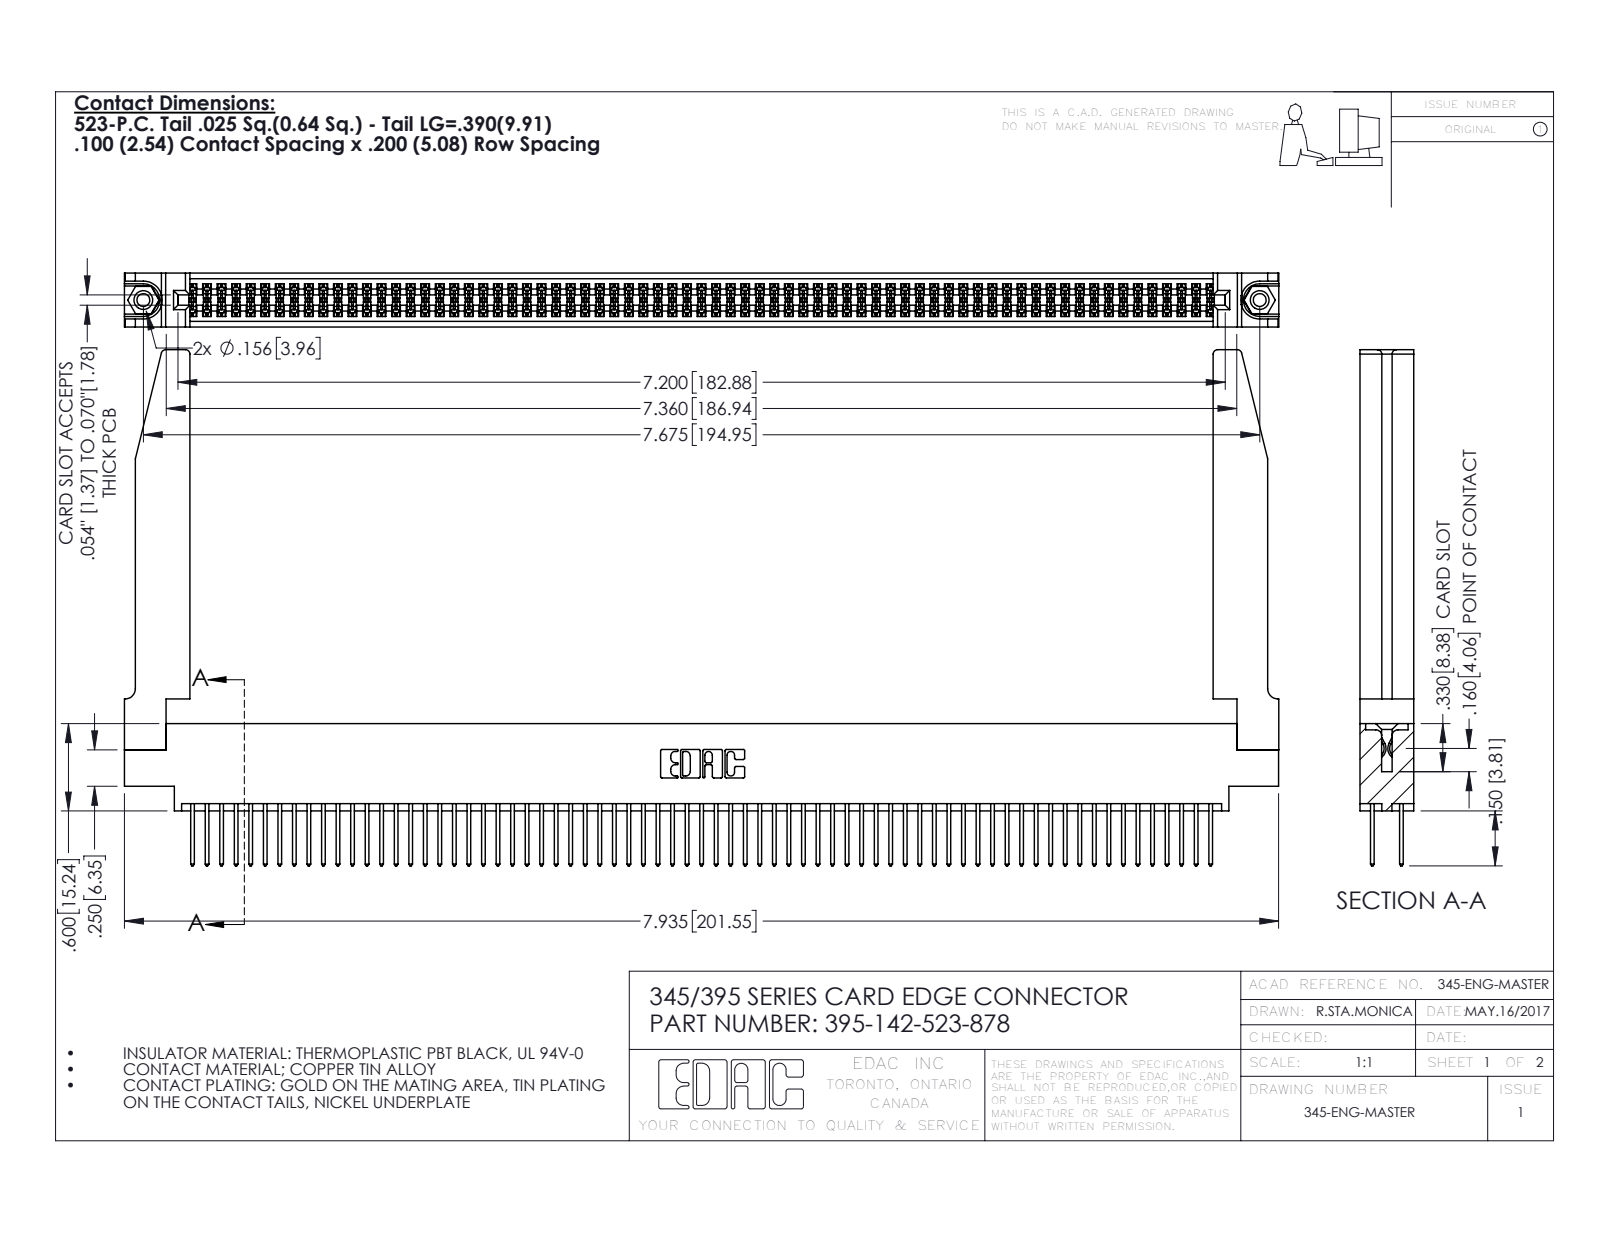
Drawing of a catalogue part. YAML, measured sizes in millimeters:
part_name: "395-142-523-878; 345-292-001_345-293-123; 345-250-001_345-250-001-102; 345-220-078_345-220-078 (+1 more)"
step_written_by: "SolidWorks 2016 (CONFIG_CONTROL_DESIGN)"
units: millimeters
bodies: {solids: 147, faces: 7464, planar: 4912, cylindrical: 2500, other: 52}
overall_size: [201.6, 90.1, 9.4]
volume: 27790
surface_area: 38450
round_holes:
  - {diameter: 2.3, count: 2}
  - {diameter: 3.2, count: 2}
  - {diameter: 4, count: 2}
  - {diameter: 1.6, count: 1}
round_bosses_or_shafts:
  - {diameter: 3.9, count: 2}
partial_cylinders:
  - {radius: 0.2, count: 213}
  - {radius: 0.3, count: 142}
  - {radius: 0.3, count: 22}
  - {radius: 0.8, count: 8}
  - {radius: 0.2, count: 6}
  - {radius: 0.8, count: 6}
  - {radius: 0.7, count: 3}
  - {radius: 0.4, count: 2}
face_to_face_distances: [1.8, 7.6, 9.4, 2.5, 6.9, 0.6, 5.1, 5.7, 4.4, 3.8]
hole_center_spacings: [6.9, 189, 194.9]
